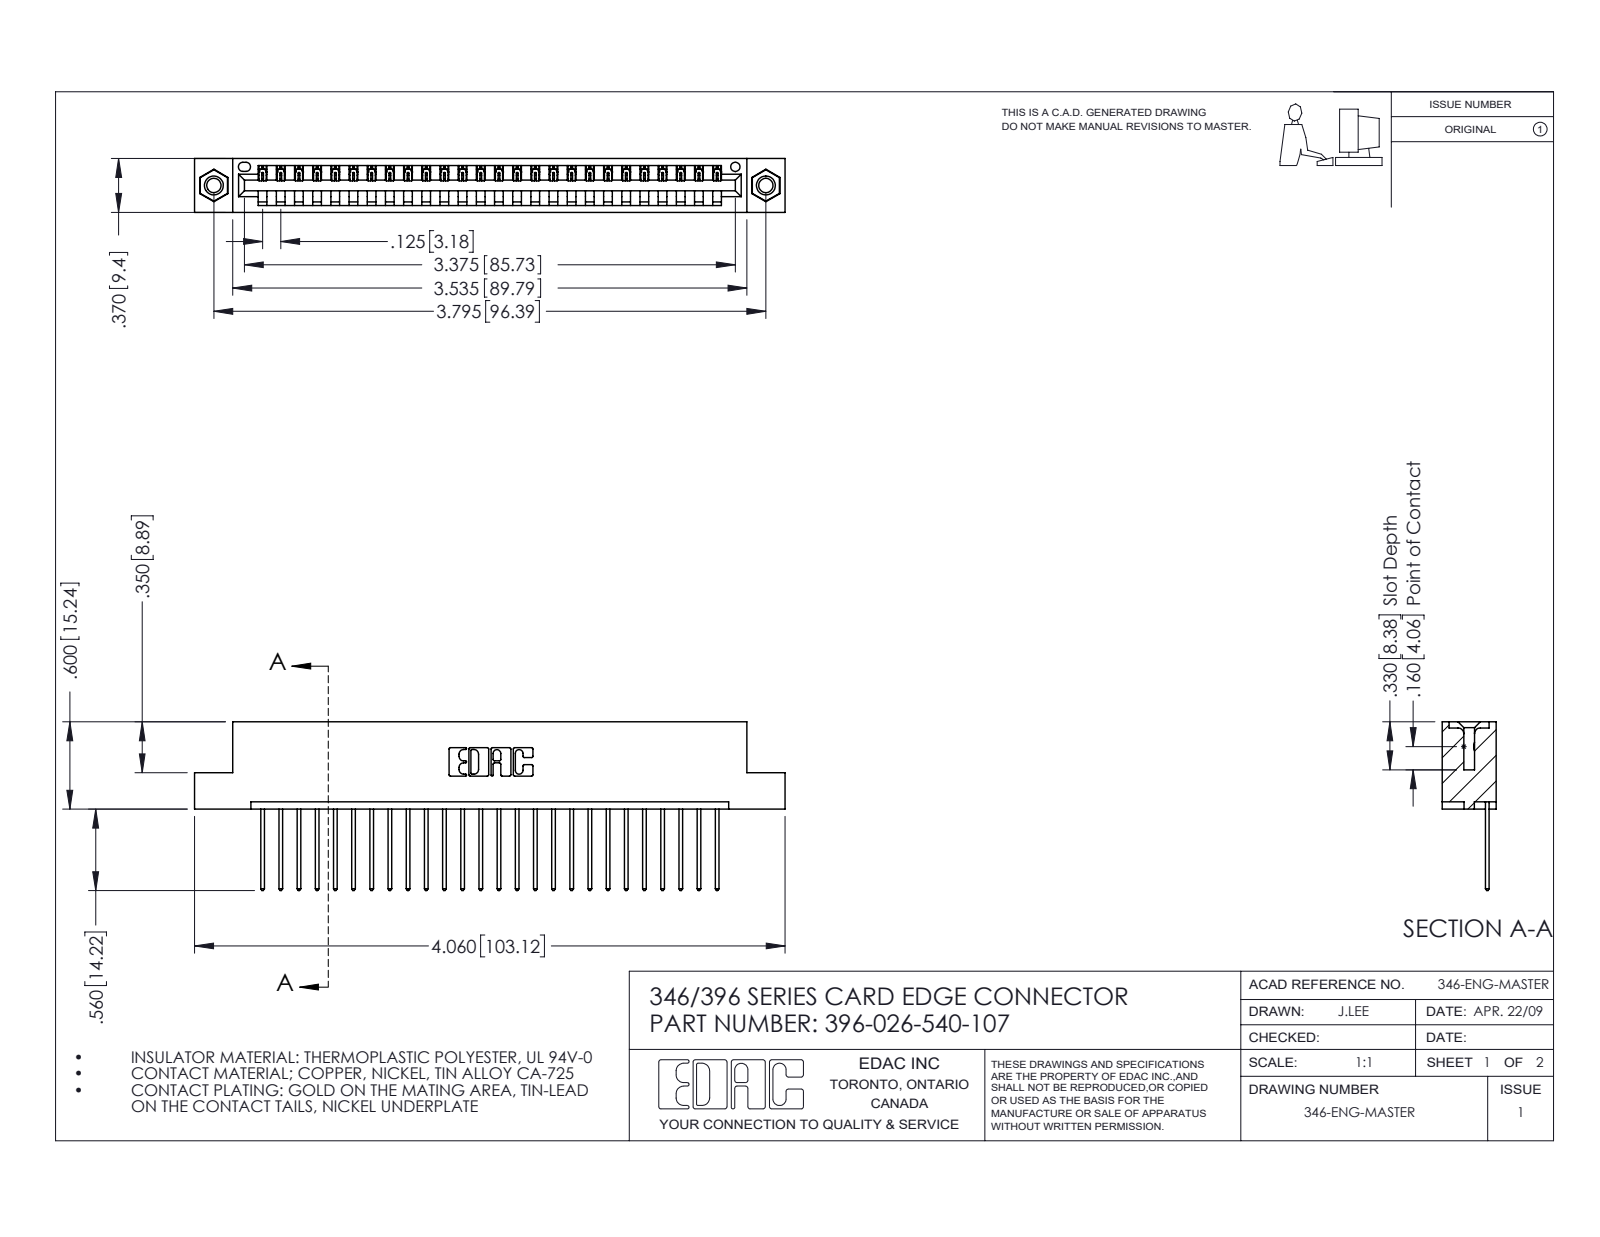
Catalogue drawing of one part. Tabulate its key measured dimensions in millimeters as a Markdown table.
| quantity | value |
| --- | --- |
| part name | 396-026-540-107; 345-292-001_345-293-140; 345-250-001_345-250-005-103; 346 Part_Flush Mounting Lugs - 0.156 Dia-TI |
| STEP written by | SolidWorks 2016 (CONFIG_CONTROL_DESIGN) |
| units | millimeters |
| bodies | 29 solids, 1690 faces (1148 planar, 526 cylindrical, 16 other) |
| overall size | 103.1 × 29.5 × 9.4 |
| volume | 9 780 mm³ |
| surface area | 12 350 mm² |
| round holes (diameter × count) | 2.5 × 2, 3.2 × 2, 4 × 2, 1.6 × 1 |
| round bosses / shafts (diameter × count) | 3.9 × 2 |
| partial cylindrical surfaces (radius × count) | 0.2 × 52, 0.3 × 52, 0.3 × 22, 0.2 × 6, 0.8 × 6, 0.7 × 3, 0.8 × 2, 1 × 2 |
| main face-to-face distances | 1.2, 8.2, 6.4, 9.4, 1.8, 7.6, 0.6, 3.8, 5.6, 2.5 |
| hole center spacings | 6.2, 91.1, 96.4 |
